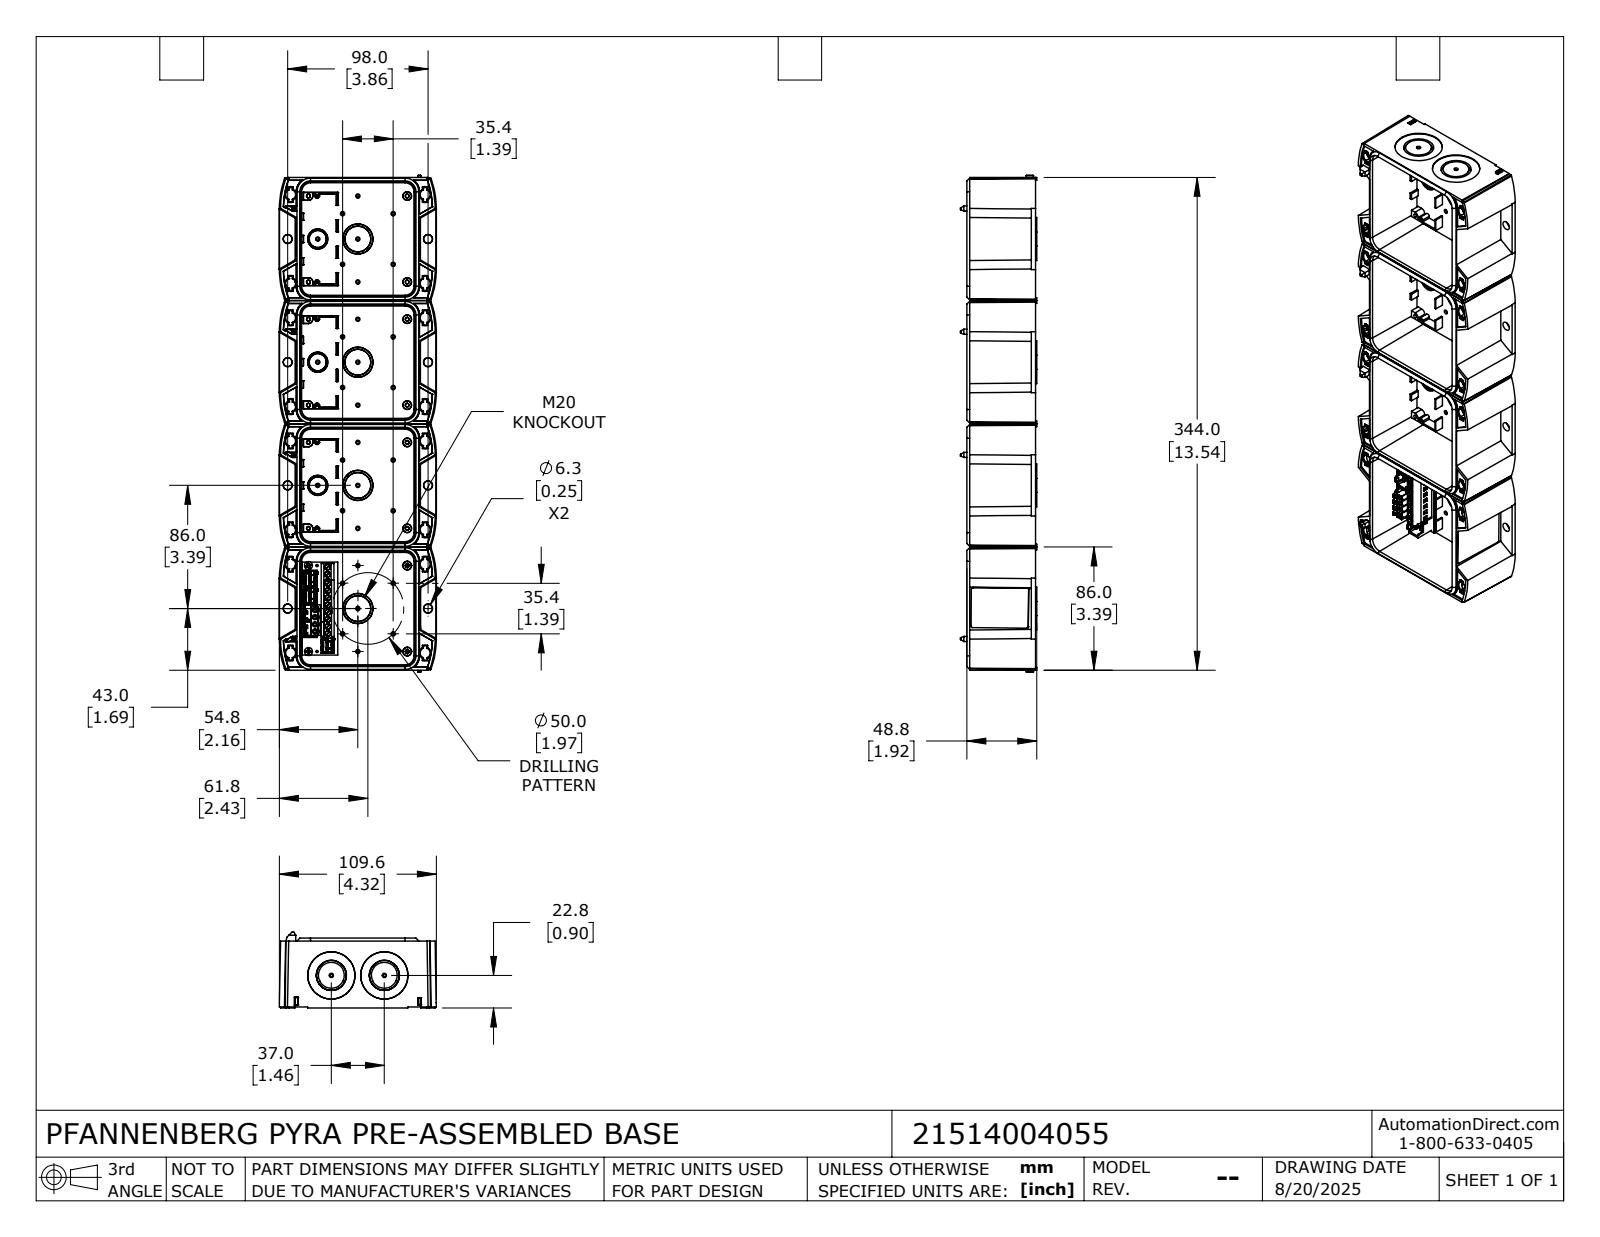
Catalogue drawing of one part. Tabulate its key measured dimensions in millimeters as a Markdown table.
| quantity | value |
| --- | --- |
| part name | 21514004055 |
| STEP written by | SolidWorks 2024 (CONFIG_CONTROL_DESIGN) |
| units | millimeters |
| bodies | 20 solids, 3800 faces (2487 planar, 427 cylindrical, 886 other) |
| overall size | 347 × 109.61 × 53.28 |
| volume | 380 398 mm³ |
| surface area | 286 723 mm² |
| round holes (diameter × count) | 4 × 18, 1 × 10, 1.4 × 10, 1.9 × 5, 1.8 × 4, 2.3 × 4, 3.6 × 4, 1.5 × 2, 3 × 2 |
| round bosses / shafts (diameter × count) | 3.8 × 18, 1.8 × 5, 5.6 × 2, 2.9 × 2 |
| partial cylindrical surfaces (radius × count) | 0.3 × 64, 1 × 15, 0.4 × 14, 0.5 × 10, 2.9 × 5, 9 × 3 |
| main face-to-face distances | 86, 172, 3, 258, 83, 85.5, 0.5, 171.5, 148.95, 74.47 |
| hole center spacings | 5, 10, 15, 11, 16, 20, 21, 6.01 |
